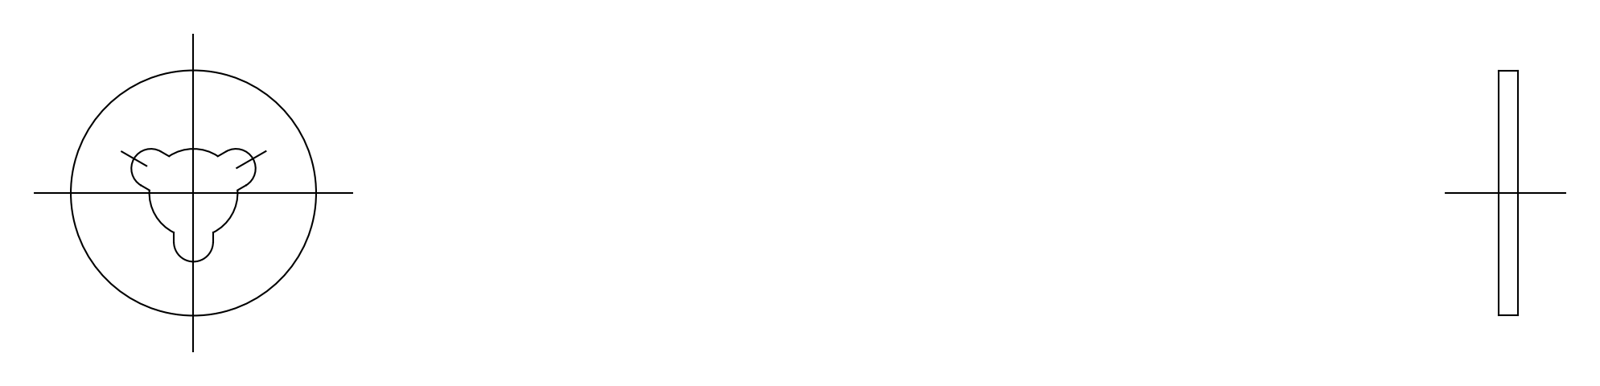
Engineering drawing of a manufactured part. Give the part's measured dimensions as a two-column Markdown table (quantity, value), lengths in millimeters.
| quantity | value |
| --- | --- |
| STEP written by | spGate 19.8.4 (****-****-****-****) (AUTOMOTIVE_DESIGN) |
| units | millimeters |
| bodies | 1 solid, 16 faces (8 planar, 8 cylindrical, 0 other) |
| overall size | 10 × 10 × 0.8 |
| volume | 51 mm³ |
| surface area | 166 mm² |
| round bosses / shafts (diameter × count) | 10 × 1 |
| partial cylindrical surfaces (radius × count) | 0.8 × 3, 1.8 × 1 |
| main face-to-face distances | 0.8, 1.6 |
